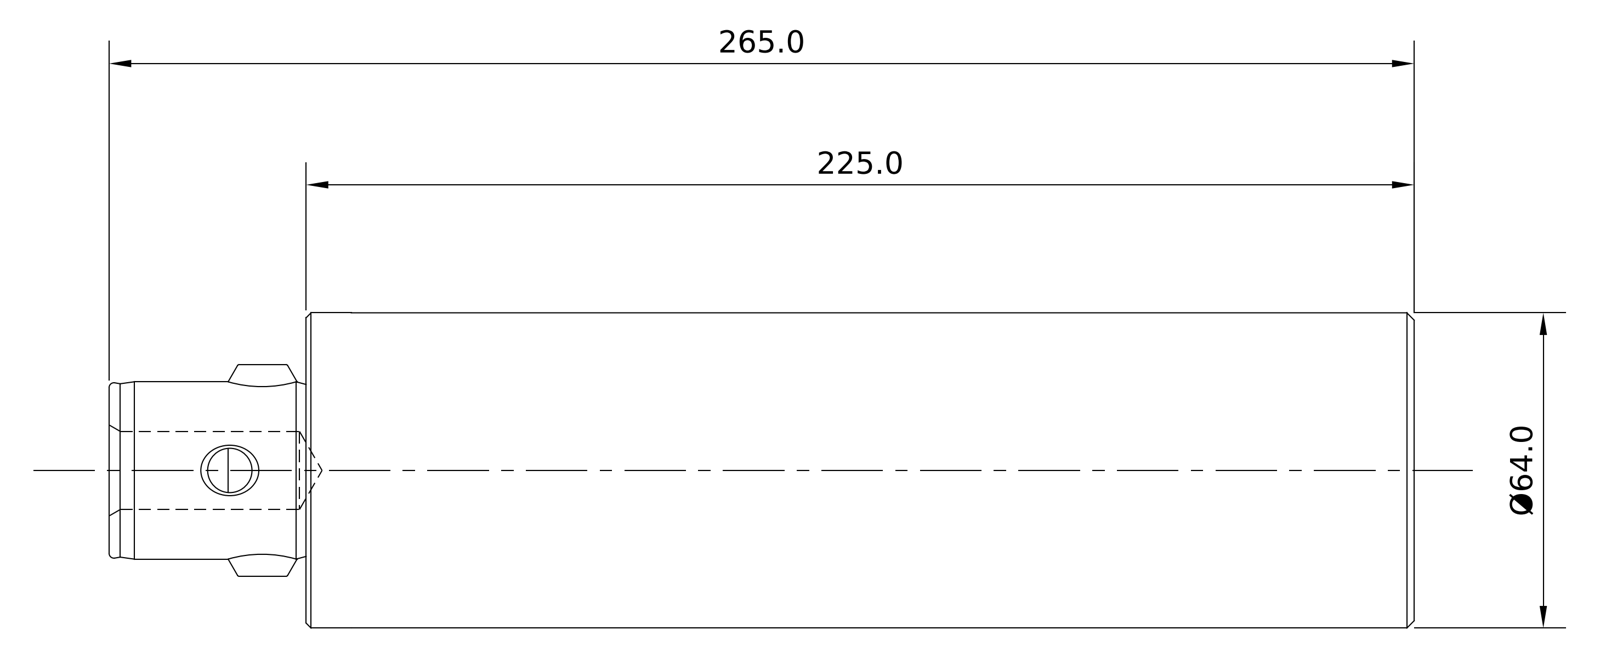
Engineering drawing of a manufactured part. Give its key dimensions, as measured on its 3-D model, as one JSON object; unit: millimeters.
{"part_name": "11.335.563; 10.691.50X_10.691.506; 691-50XRing_10.691.506Ring", "step_written_by": "SolidWorks 2012 (AUTOMOTIVE_DESIGN)", "units": "millimeters", "bodies": {"solids": 3, "faces": 87, "planar": 19, "cylindrical": 31, "other": 37}, "overall_size": [265, 63.5, 63.5], "volume_mm3": 746044, "surface_area_mm2": 60187, "round_holes": [[4.76, 1], [9, 1], [14, 1], [16, 1], [18.5, 1]], "round_bosses_or_shafts": [[63.5, 1], [36, 1], [13.9, 1], [11.9, 1], [9.9, 1]], "partial_cylinders_radius": [[18, 1]], "face_to_face_distances": [225, 40, 265, 43, 15.2, 27.8, 20.2, 5, 22.8, 3]}
